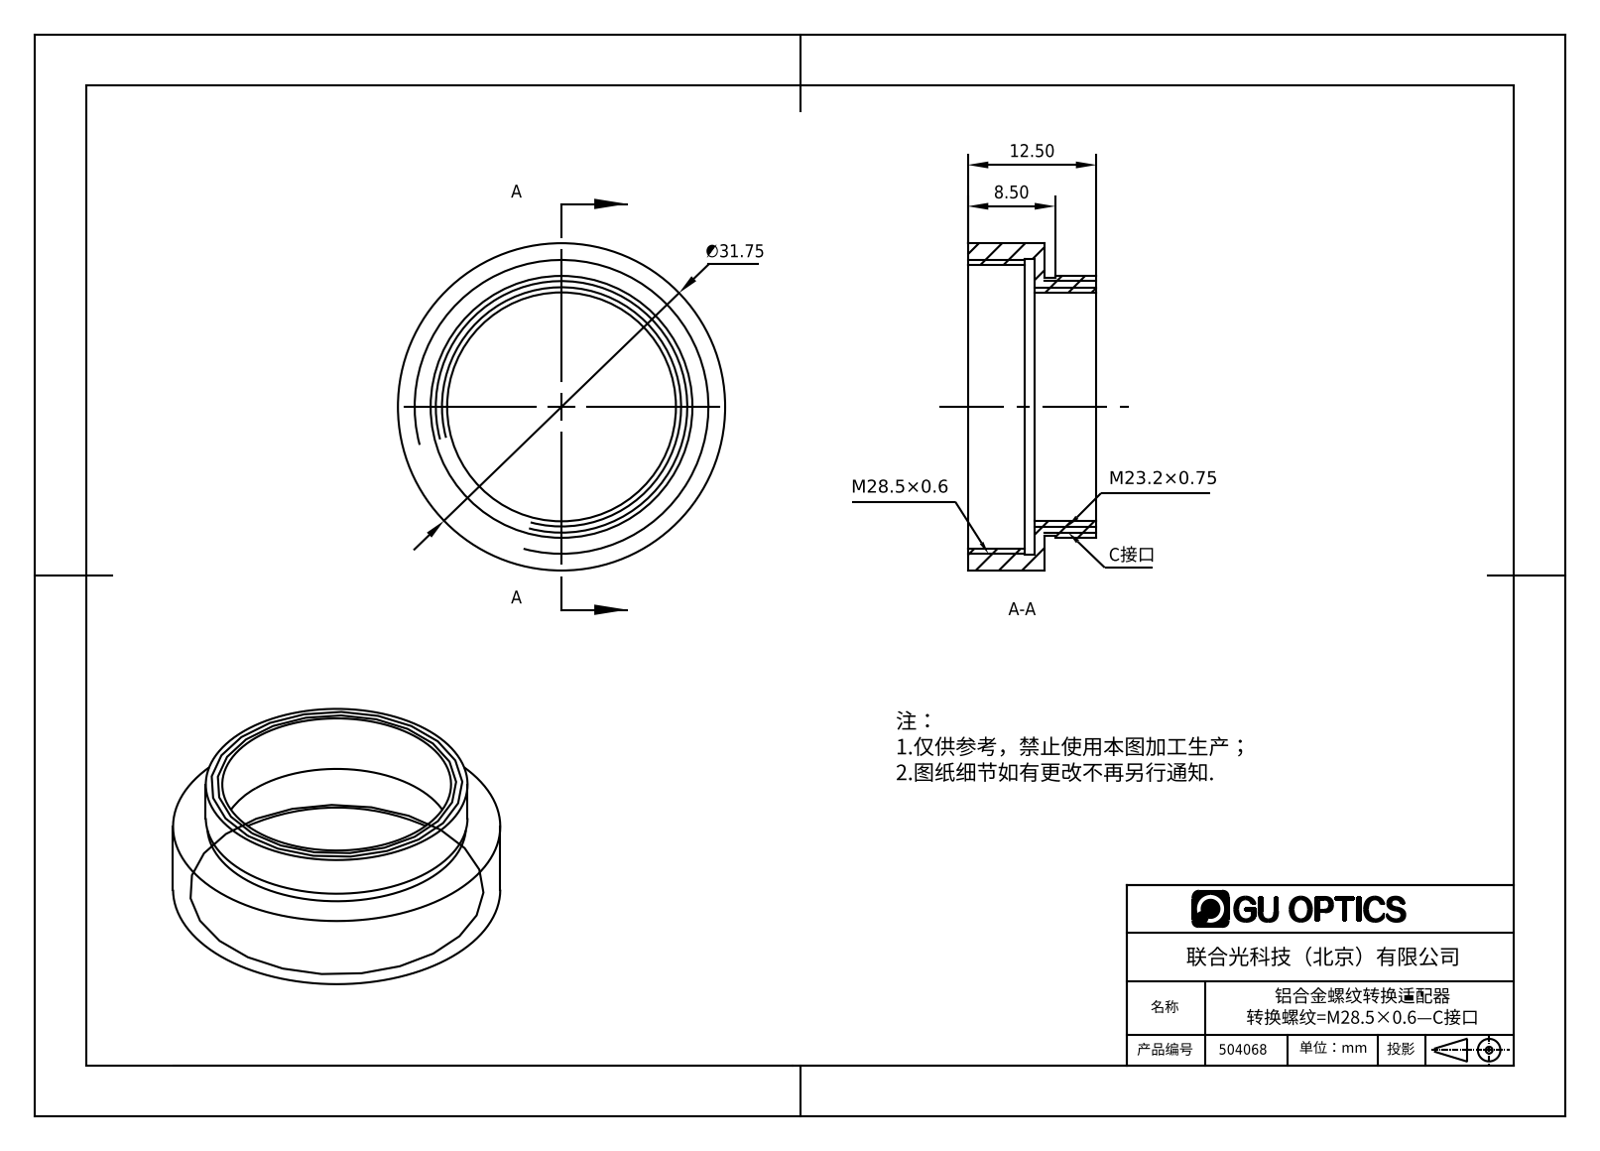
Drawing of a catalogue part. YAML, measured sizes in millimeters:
part_name: "504068"
step_written_by: "SolidWorks 2016 (AUTOMOTIVE_DESIGN)"
units: millimeters
bodies: {solids: 1, faces: 18, planar: 6, cylindrical: 12, other: 0}
overall_size: [31.75, 31.75, 12.5]
volume: 2223
surface_area: 3069
round_holes:
  - {diameter: 22.2, count: 1}
  - {diameter: 27.5, count: 1}
  - {diameter: 28.7, count: 1}
round_bosses_or_shafts:
  - {diameter: 31.75, count: 1}
  - {diameter: 25.4, count: 1}
  - {diameter: 25.1, count: 1}
face_to_face_distances: [1, 6.5, 7.5, 12.5, 6, 5, 2, 5.5, 7, 8.5]
